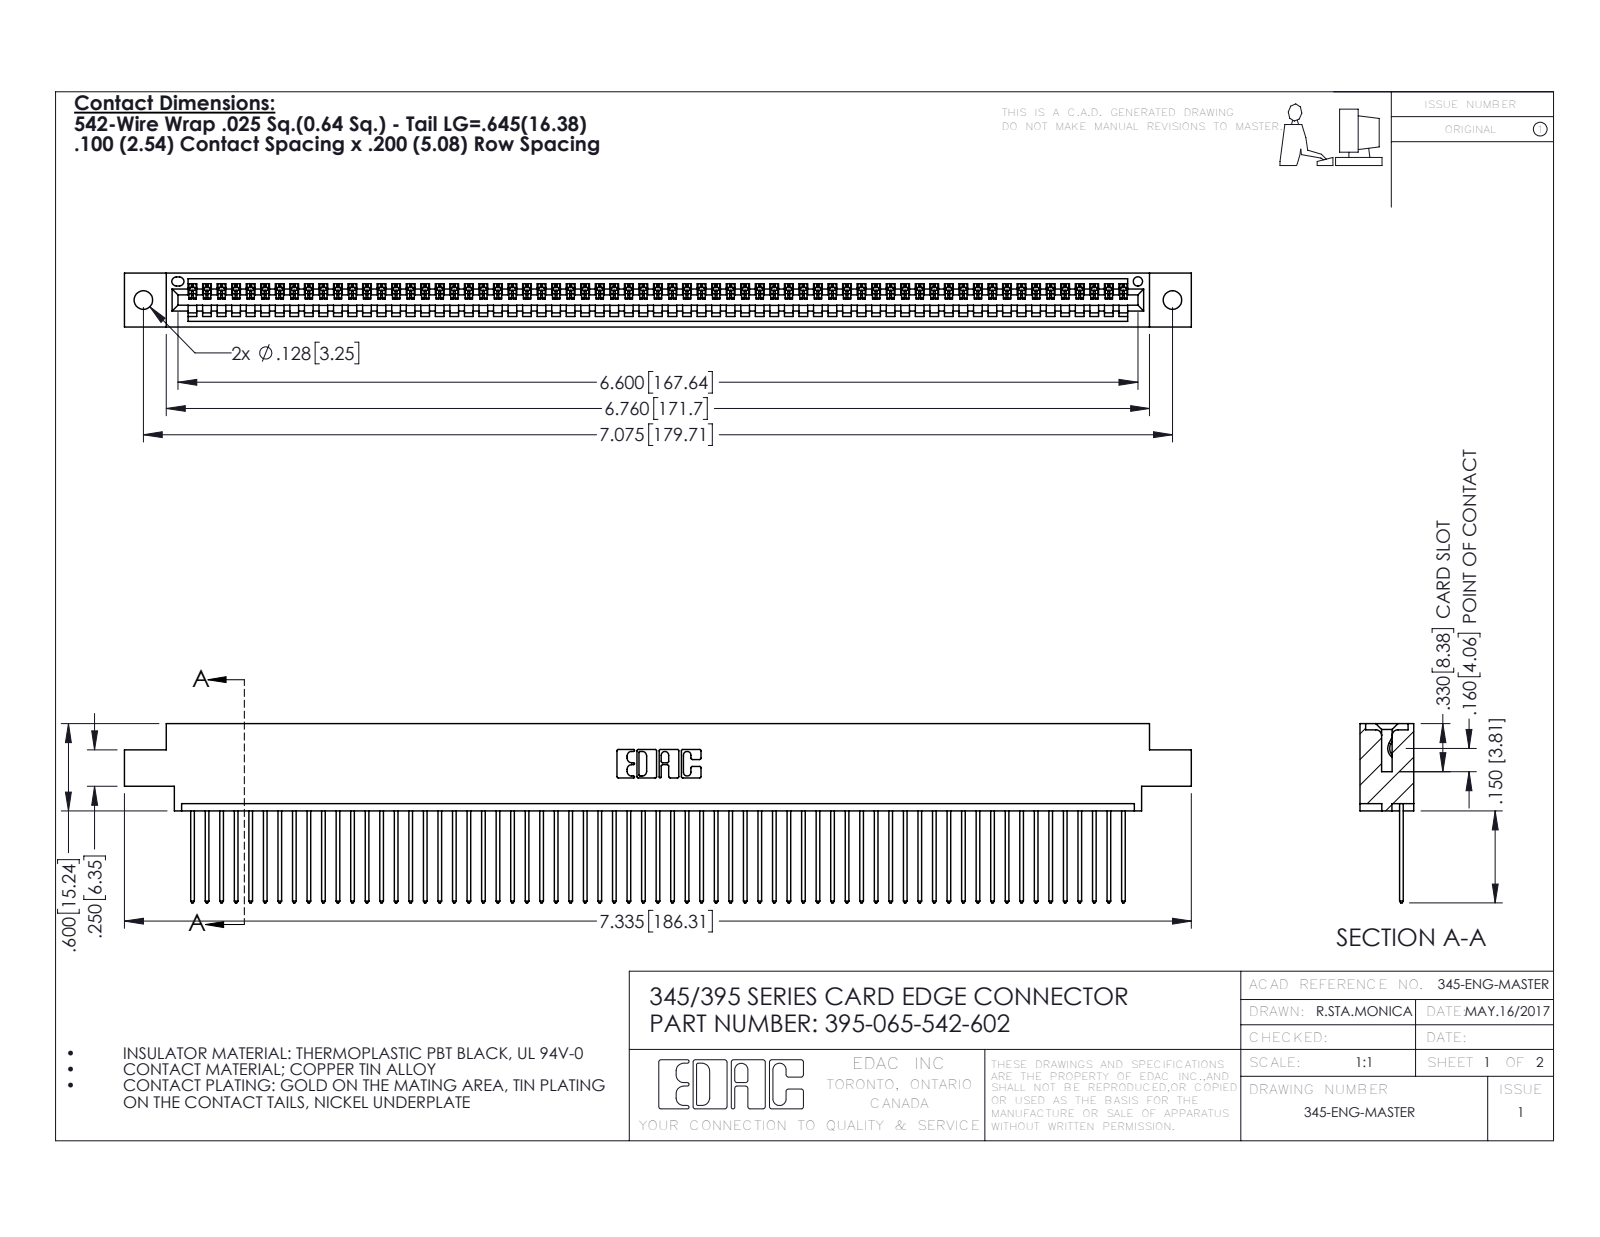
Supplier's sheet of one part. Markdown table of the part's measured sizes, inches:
| quantity | value |
| --- | --- |
| part name | 395-065-542-602; 345 Part_0.170 Offset - 0.128 Dia; 345-292-001_345-293-142 |
| STEP written by | SolidWorks 2016 (CONFIG_CONTROL_DESIGN) |
| units | inches |
| bodies | 66 solids, 3900 faces (2684 planar, 1216 cylindrical, 0 other) |
| overall size | 7.335 × 1.232 × 0.37 |
| volume | 1.091 in³ |
| surface area | 38.5 in² |
| round holes (diameter × count) | 0.128 × 2, 0.064 × 1 |
| partial cylindrical surfaces (radius × count) | 0.006 × 130, 0.01 × 130, 0.01 × 22, 0.007 × 6, 0.031 × 6, 0.026 × 3, 0.031 × 2, 0.04 × 2 |
| main face-to-face distances | 0.072, 0.298, 0.37, 0.098, 0.272, 0.025, 0.2, 0.225, 0.175, 0.149 |
| hole center spacings | 0.27, 6.839, 7.075 |
